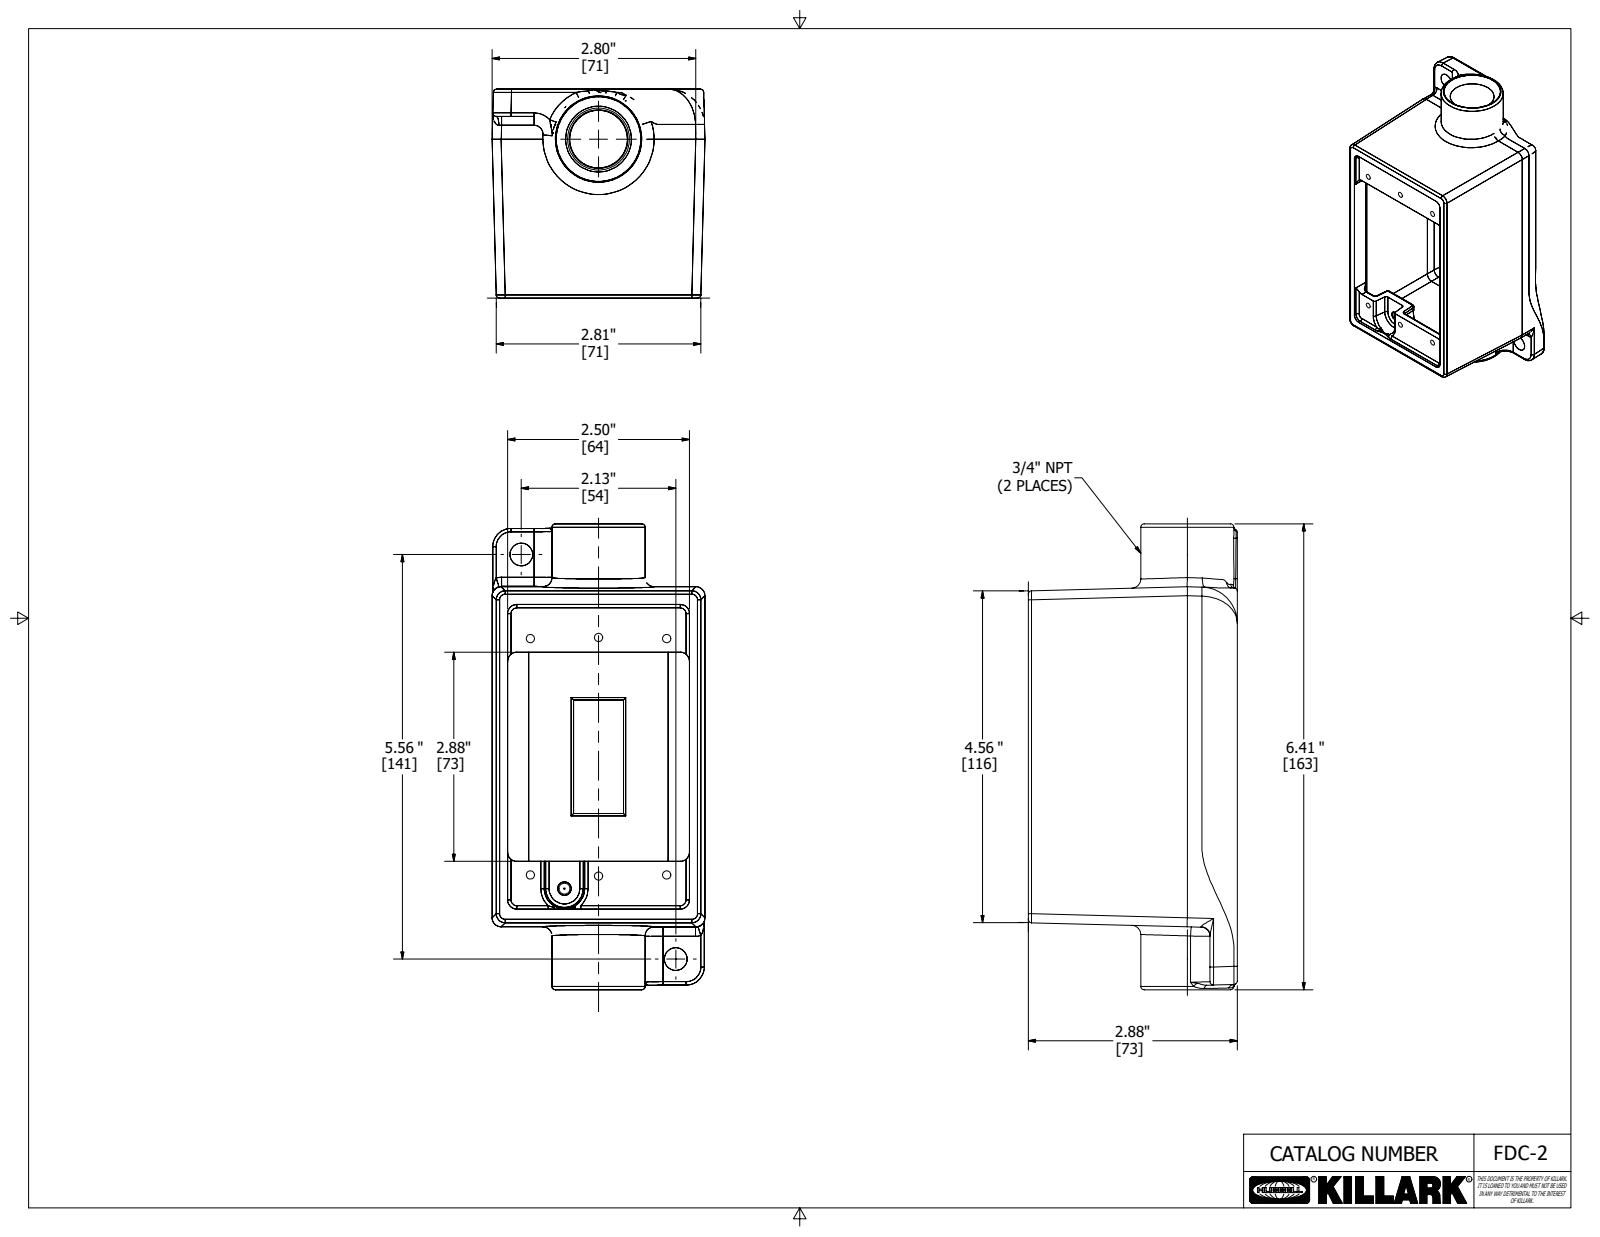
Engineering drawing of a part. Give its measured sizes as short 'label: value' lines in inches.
name: 17578-3; 17578-1
written by: Autodesk Inventor 2020 (AUTOMOTIVE_DESIGN)
unit: in
bodies: 1 solid, 257 faces (63 planar, 94 cylindrical, 100 other)
size: 6.406 × 2.927 × 2.875
volume: 10.29 in³; area: 121.9 in²
holes: 6× ⌀0.113, 2× ⌀0.312, 1× ⌀0.15, 1× ⌀0.792, 1× ⌀0.903
bosses: 1× ⌀1.281
rounds: 32× R0.125, 12× R0.047, 9× R0.031, 8× R0.047, 4× R0.25, 4× R0.344, 2× R0.062, 1× R0.094
face distances: 0.156, 0.156, 2.77, 2.781, 2.625, 2.927, 0.031, 2.625, 2.469, 2.875
hole spacings: 0.937, 1.163, 1.875, 2.31, 3.25, 3.397, 3.398, 3.752
